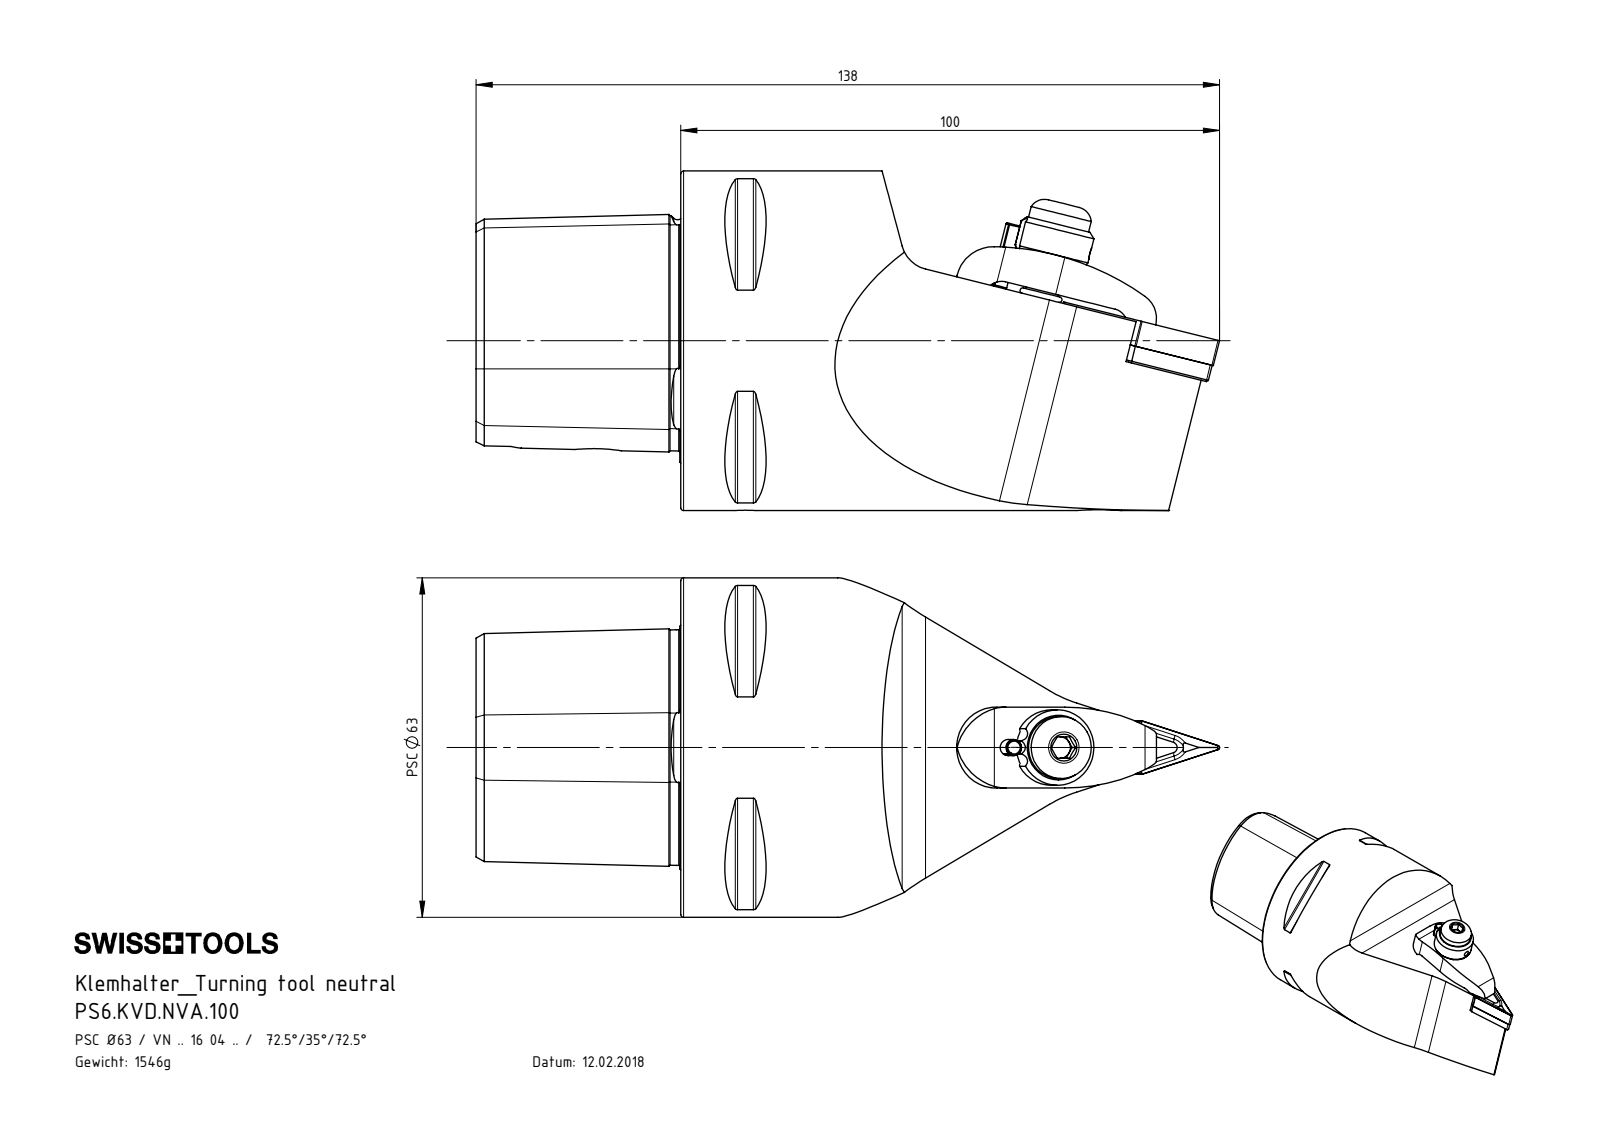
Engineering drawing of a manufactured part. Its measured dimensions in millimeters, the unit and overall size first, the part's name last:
Units: millimetres
Overall size (bounding box): 138 × 63 × 63
Round holes (diameter × count): ⌀2 ×3, ⌀5 ×3, ⌀7 ×2, ⌀8.5 ×2, ⌀2.4 ×1, ⌀3 ×1, ⌀3.3 ×1, ⌀3.8 ×1, ⌀4 ×1, ⌀4.95 ×1, ⌀6 ×1, ⌀6.2 ×1
Round bosses / shafts (diameter × count): ⌀6 ×2, ⌀3 ×2, ⌀63 ×1, ⌀14 ×1, ⌀11.5 ×1, ⌀7 ×1, ⌀6.8 ×1, ⌀6.2 ×1
Partial cylindrical surfaces — rounded edges, fillets, slot ends (radius × count): R0.5 ×10, R0.39 ×6, R0.69 ×6, R0.4 ×4, R1.5 ×3, R2 ×2, R3 ×2, R6 ×2
Main face-to-face distances: 8.94, 38, 24.88, 4.46, 5.76, 1.3, 3.18, 7.64, 27, 11
Hole centre spacings: 27.32, 8.02, 8.2, 19.12, 19.3, 19.31, 8.01, 27.5
Volume: 196 457 mm³ · Surface area: 35 793 mm²
Bodies: 11 solids, 425 faces (99 planar, 132 cylindrical, 194 other)
Part name (STEP PRODUCT): PS6-KVD.NVA.100; KVT_MB_600_060; ISO 13337 - 3 x 12_PreviewCfg; WCC-ER4.103.032_A (+7 more)
STEP written by: SolidWorks 2012 (CONFIG_CONTROL_DESIGN)
